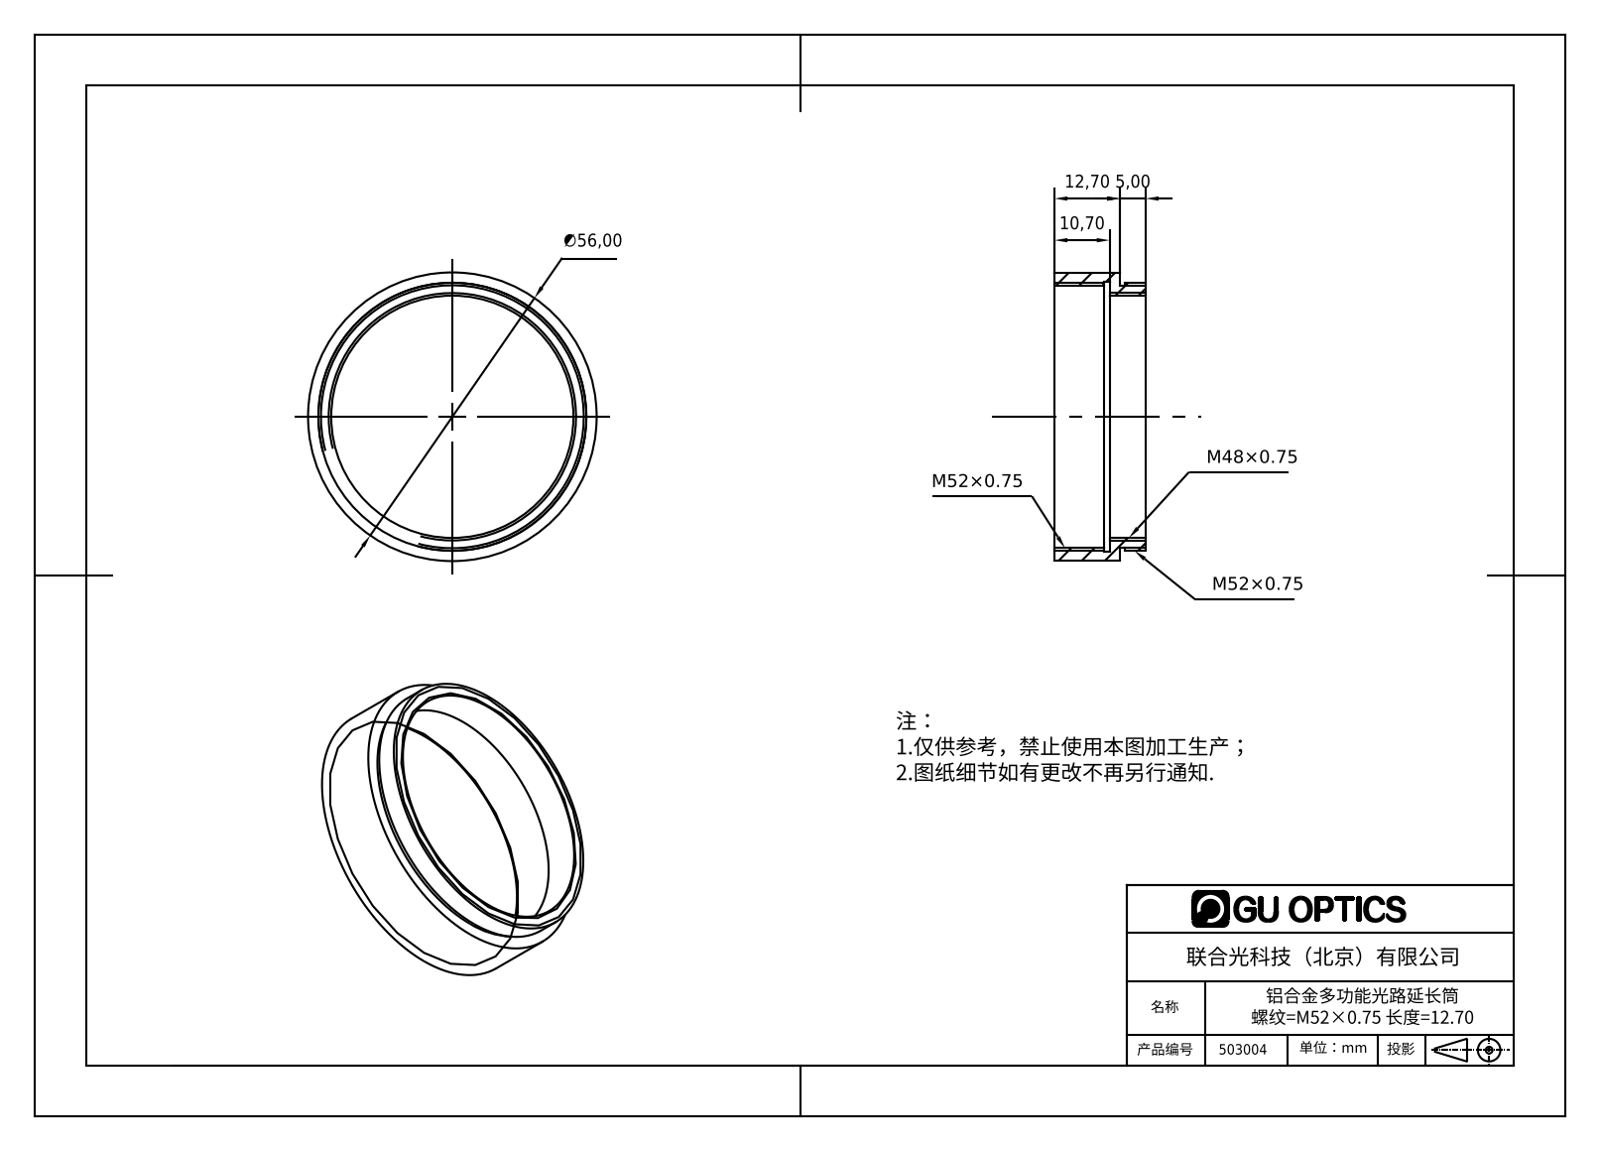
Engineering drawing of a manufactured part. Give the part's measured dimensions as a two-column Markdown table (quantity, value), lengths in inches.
| quantity | value |
| --- | --- |
| part name | 503004 |
| STEP written by | SolidWorks 2016 (AUTOMOTIVE_DESIGN) |
| units | inches |
| bodies | 1 solid, 18 faces (6 planar, 12 cylindrical, 0 other) |
| overall size | 2.205 × 2.205 × 0.697 |
| volume | 0.471 in³ |
| surface area | 11.8 in² |
| round holes (diameter × count) | 1.85 × 1, 2.008 × 1, 2.055 × 1 |
| round bosses / shafts (diameter × count) | 2.205 × 1, 2.047 × 1 |
| main face-to-face distances | 0.5, 0.421, 0.079, 0.697, 0.276, 0.197, 0.039, 0.118, 0.157, 0.382 |
